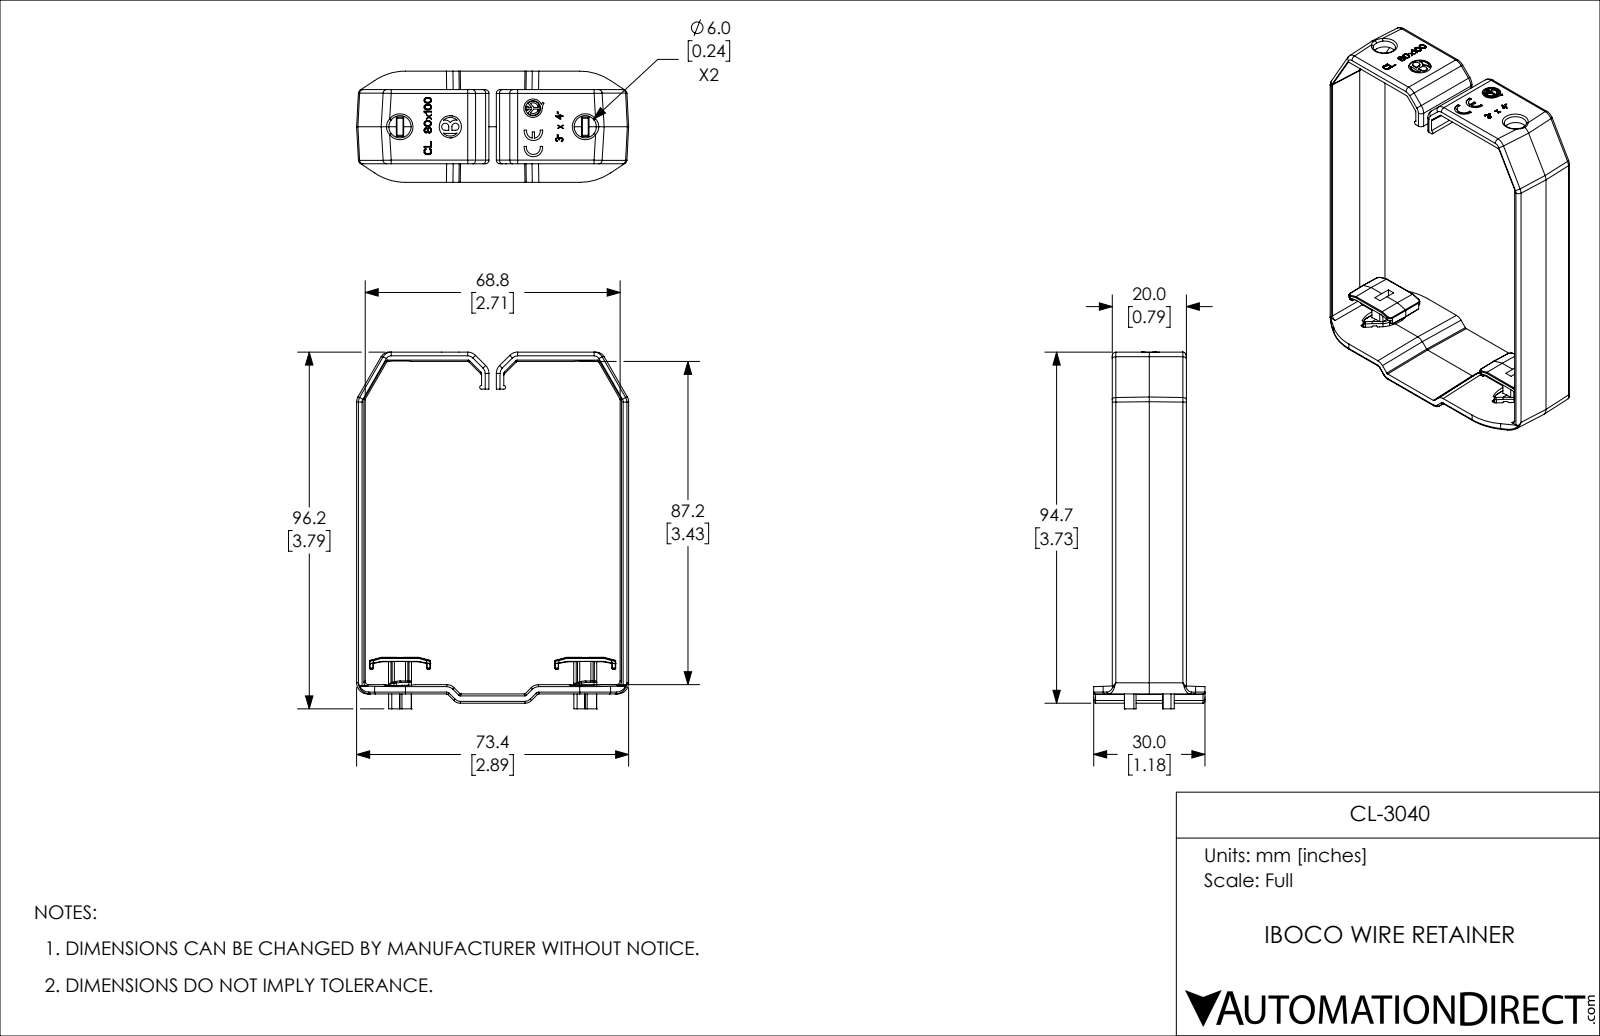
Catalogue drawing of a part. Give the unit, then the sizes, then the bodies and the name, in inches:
Units: inches
Overall size (bounding box): 3.787 × 2.89 × 1.181
Round holes (diameter × count): ⌀0.236 ×3, ⌀0.197 ×1
Round bosses / shafts (diameter × count): ⌀0.161 ×1
Partial cylindrical surfaces — rounded edges, fillets, slot ends (radius × count): R0.02 ×48, R0.008 ×36, R0.039 ×34, R0.098 ×20, R0.012 ×12, R0.016 ×12, R0.118 ×8, R0.026 ×4
Main face-to-face distances: 2.706, 2.887, 0.098, 3.43, 3.63, 3.528, 3.728, 0.079, 0.157, 0.047
Hole centre spacings: 0.535, 0.589, 0.9, 1.427, 1.434, 1.969
Volume: 0.895 in³ · Surface area: 26.01 in²
Bodies: 1 solid, 975 faces (653 planar, 255 cylindrical, 67 other)
Part name (STEP PRODUCT): CL-3040
STEP written by: SolidWorks 2019 (CONFIG_CONTROL_DESIGN)
